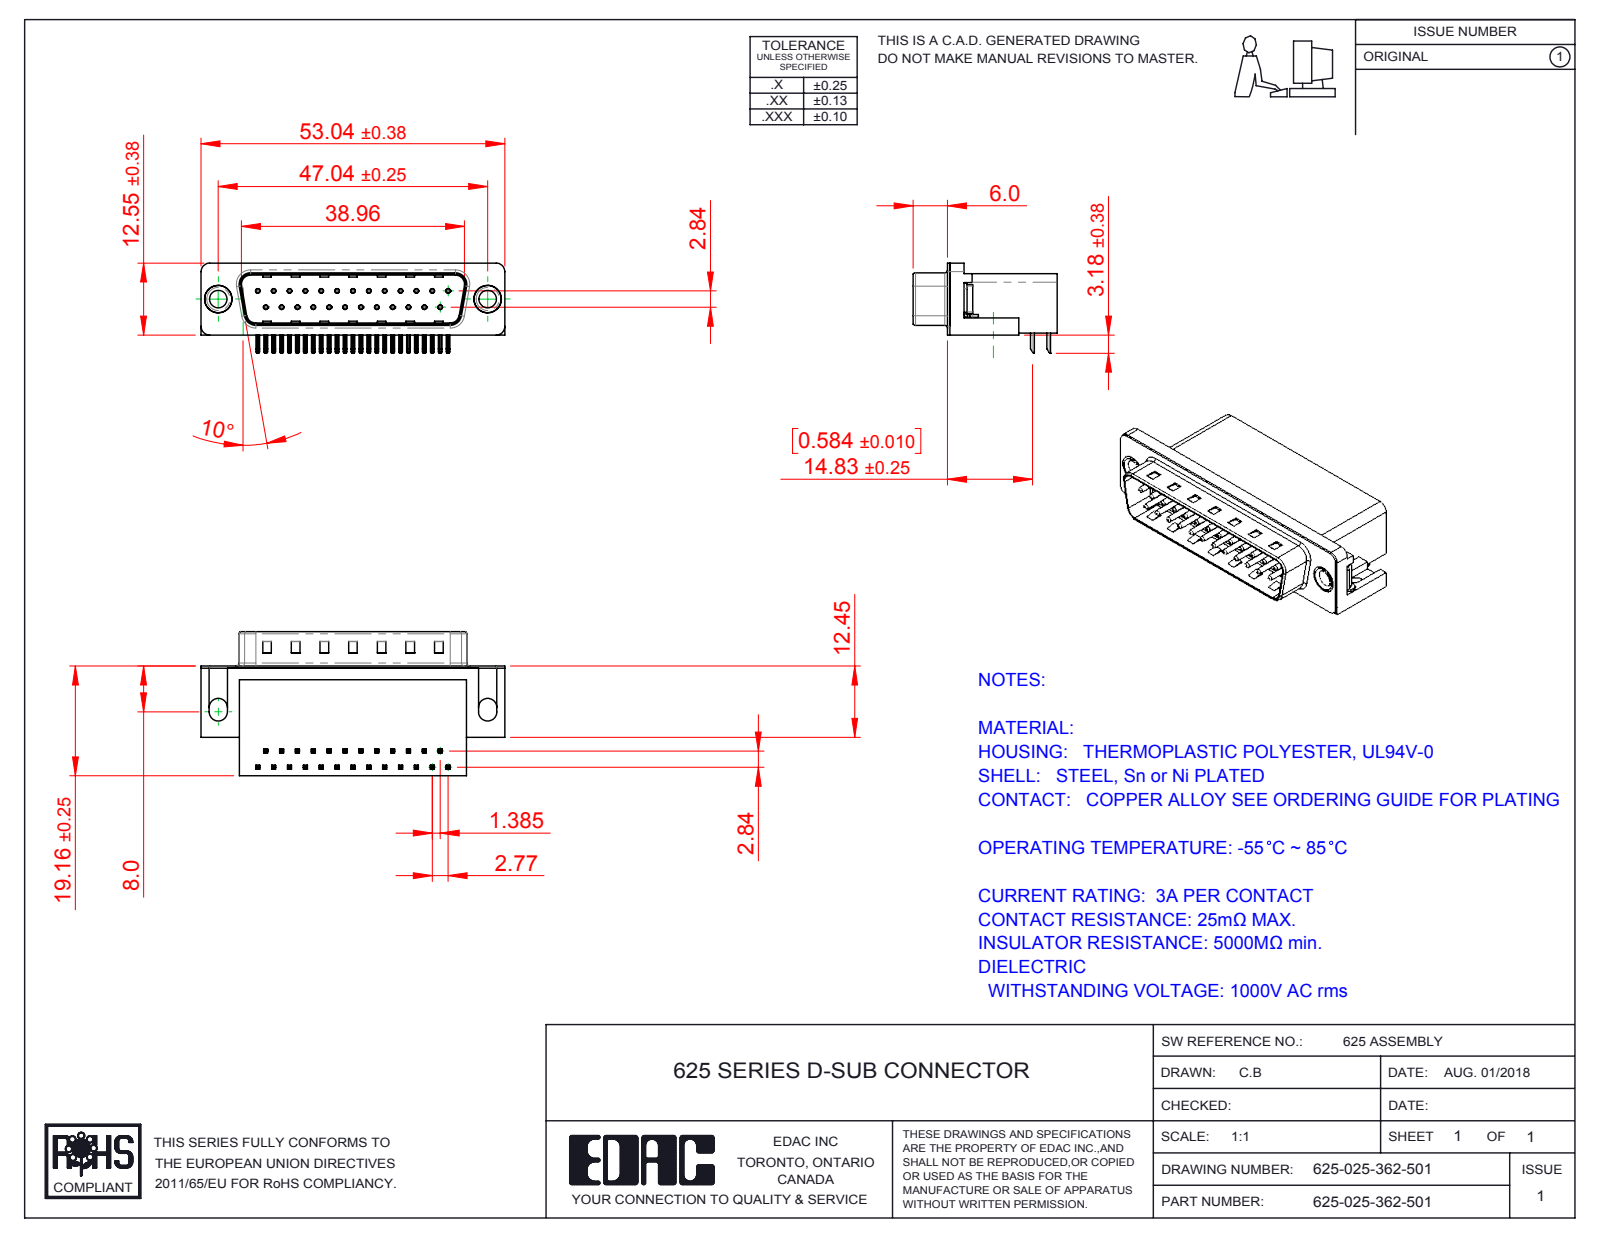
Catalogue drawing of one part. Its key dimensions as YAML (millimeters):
part_name: "625 Housing_25 Socket; 625 Shell_25 Socket; 625 Non Board Mount; 625 Thru Hole Rivet (+3 more)"
step_written_by: "SolidWorks 2016 (CONFIG_CONTROL_DESIGN)"
units: millimeters
bodies: {solids: 31, faces: 2223, planar: 1407, cylindrical: 639, other: 177}
overall_size: [53.04, 25.16, 15.73]
volume: 9125
surface_area: 8704
round_holes:
  - {diameter: 0.35, count: 25}
  - {diameter: 0.8, count: 25}
  - {diameter: 3.05, count: 2}
  - {diameter: 4, count: 2}
  - {diameter: 4.8, count: 2}
  - {diameter: 5, count: 2}
round_bosses_or_shafts:
  - {diameter: 0.75, count: 25}
  - {diameter: 4.9, count: 2}
  - {diameter: 4.75, count: 2}
  - {diameter: 3.85, count: 2}
partial_cylinders:
  - {radius: 0.25, count: 108}
  - {radius: 0.12, count: 50}
  - {radius: 1, count: 16}
  - {radius: 0.5, count: 9}
  - {radius: 1.6, count: 8}
  - {radius: 1.5, count: 7}
  - {radius: 0.9, count: 4}
  - {radius: 2, count: 4}
face_to_face_distances: [0.4, 10.35, 18.76, 2.1, 8.76, 10.46, 10.86, 1.7, 19.16, 10.11]
hole_center_spacings: [3.16, 2.77, 11.08, 5.54, 8.31, 5.03, 13.85, 7.48]
